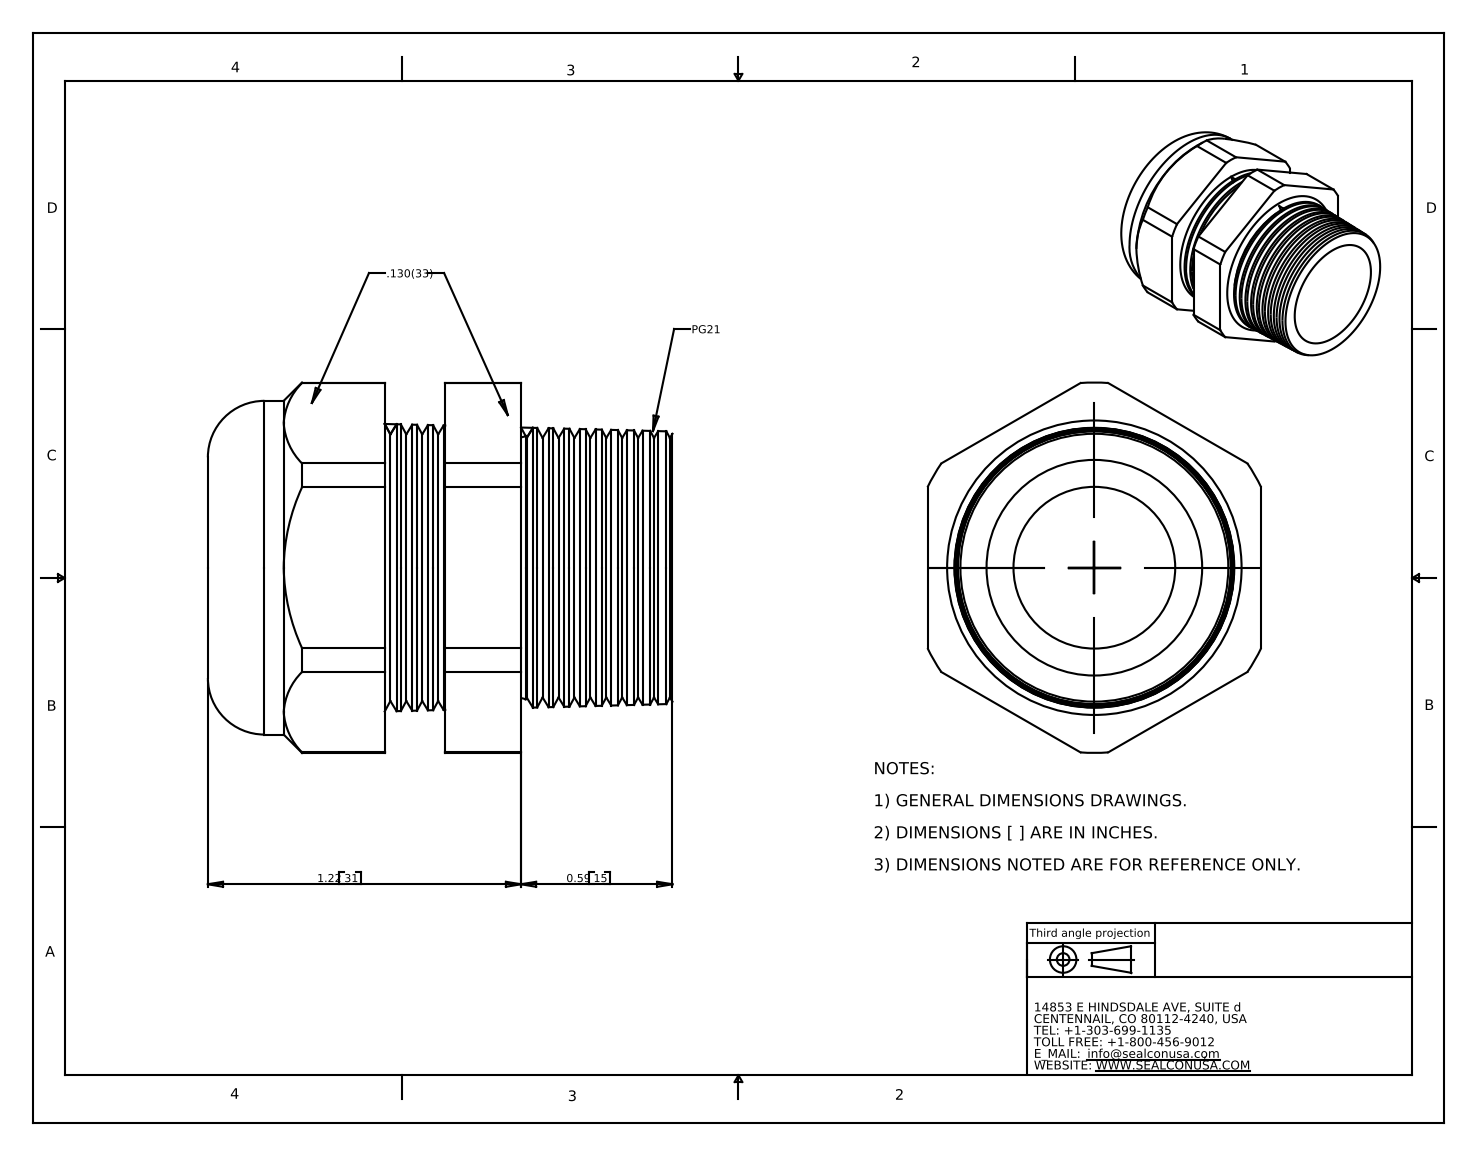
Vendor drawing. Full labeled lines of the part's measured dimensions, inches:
Part name (STEP PRODUCT): CD21CR-BK
STEP written by: SolidWorks 2007 (CONFIG_CONTROL_DESIGN)
Units: inches
Bodies: 2 solids, 140 faces (20 planar, 22 cylindrical, 98 other)
Overall size (bounding box): 1.81 × 1.443 × 1.3
Volume: 1.379 in³ · Surface area: 17.28 in²
Round holes (diameter × count): ⌀0.63 ×1, ⌀0.84 ×1
Round bosses / shafts (diameter × count): ⌀1.3 ×1
Partial cylindrical surfaces — rounded edges, fillets, slot ends (radius × count): R0.721 ×1
Main face-to-face distances: 1.3, 0.63, 0.394, 0.236, 0.295, 0.925, 0.531, 1.515, 1.121, 0.885
